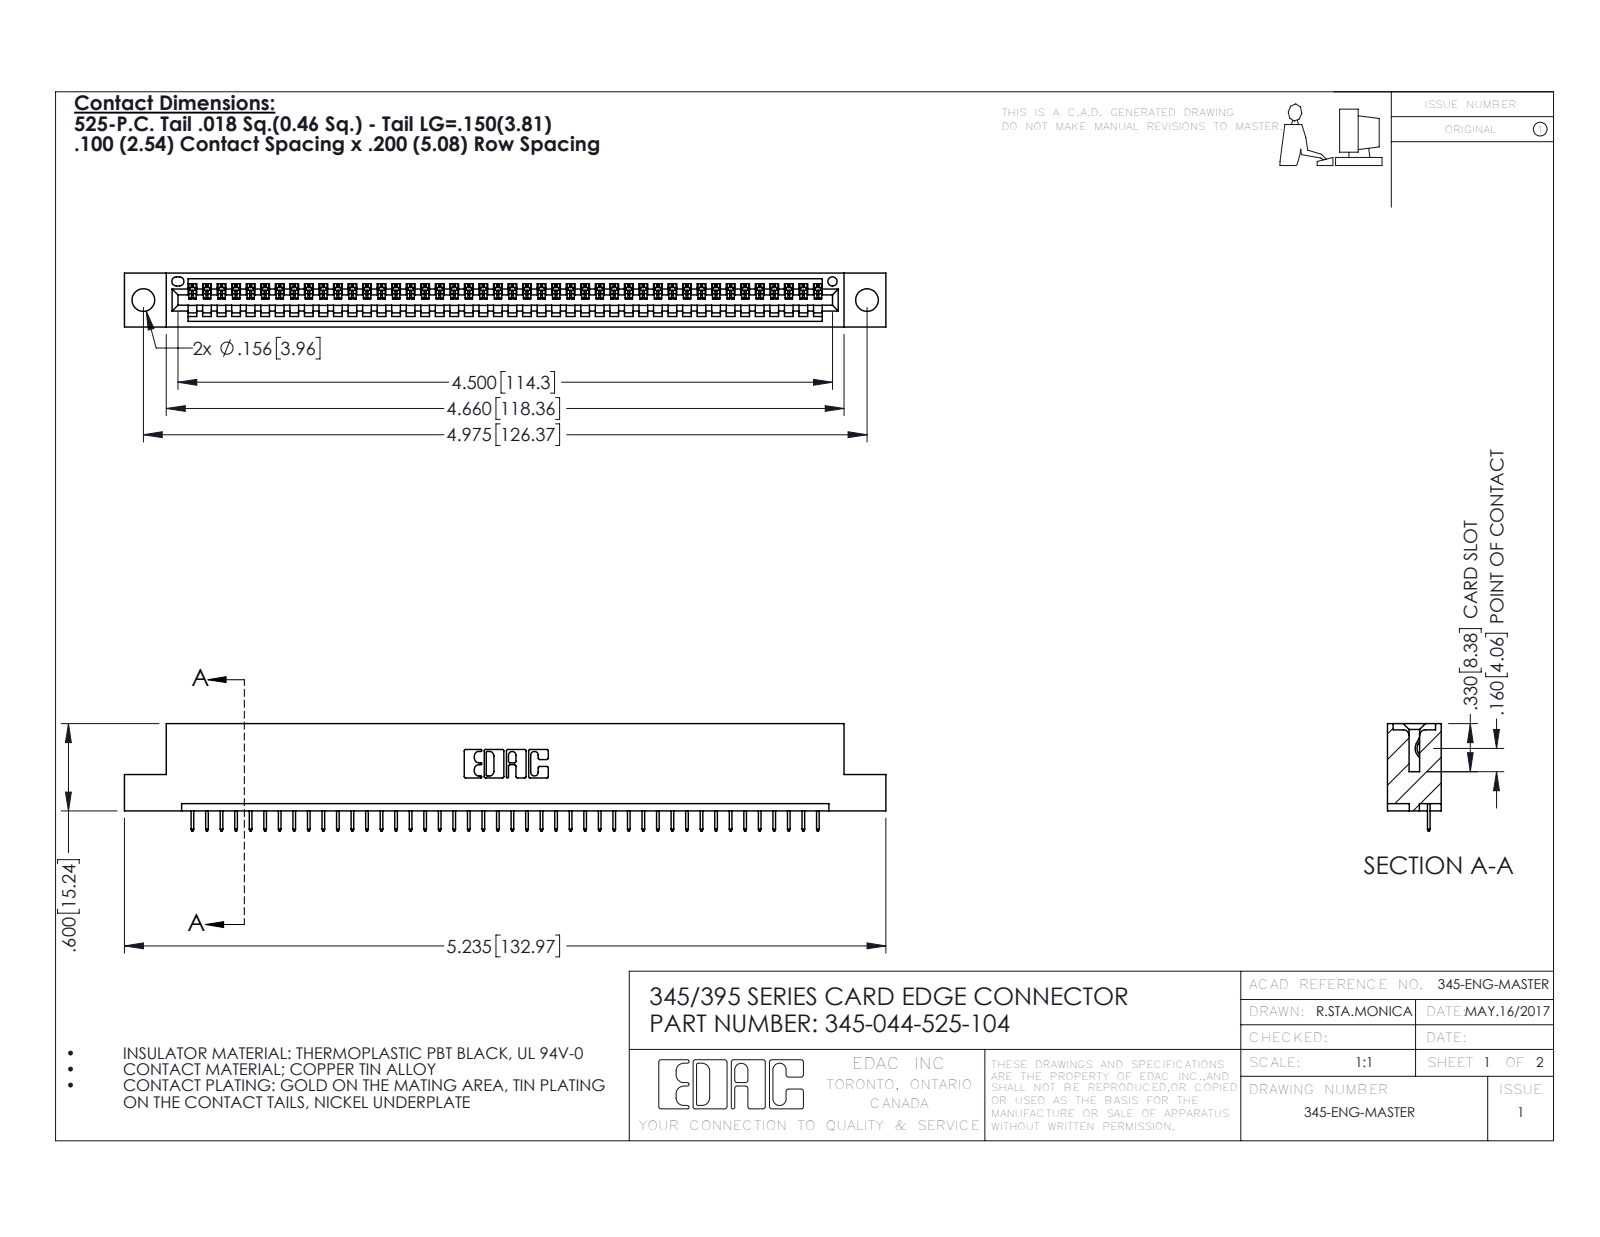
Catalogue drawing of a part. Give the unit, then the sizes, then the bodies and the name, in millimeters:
Units: millimetres
Overall size (bounding box): 133 × 18.7 × 9.4
Round holes (diameter × count): ⌀4 ×2, ⌀1.6 ×1
Partial cylindrical surfaces — rounded edges, fillets, slot ends (radius × count): R0.2 ×88, R0.3 ×22, R0.2 ×6, R0.8 ×6, R0.7 ×3, R0.8 ×2, R1 ×2, R0.4 ×1
Main face-to-face distances: 7.6, 1.8, 9.4, 5.1, 2.5, 6.9, 0.6, 5.7, 1.8, 3.8
Hole centre spacings: 6.9, 120.4, 126.4
Volume: 12 400 mm³ · Surface area: 15 680 mm²
Bodies: 45 solids, 2854 faces (2104 planar, 750 cylindrical, 0 other)
Part name (STEP PRODUCT): 345 Part_Flush Mounting Lugs - 0.156 Dia-TH; 345-044-525-104; 345-292-001_345-293-125
STEP written by: SolidWorks 2020 (CONFIG_CONTROL_DESIGN)
